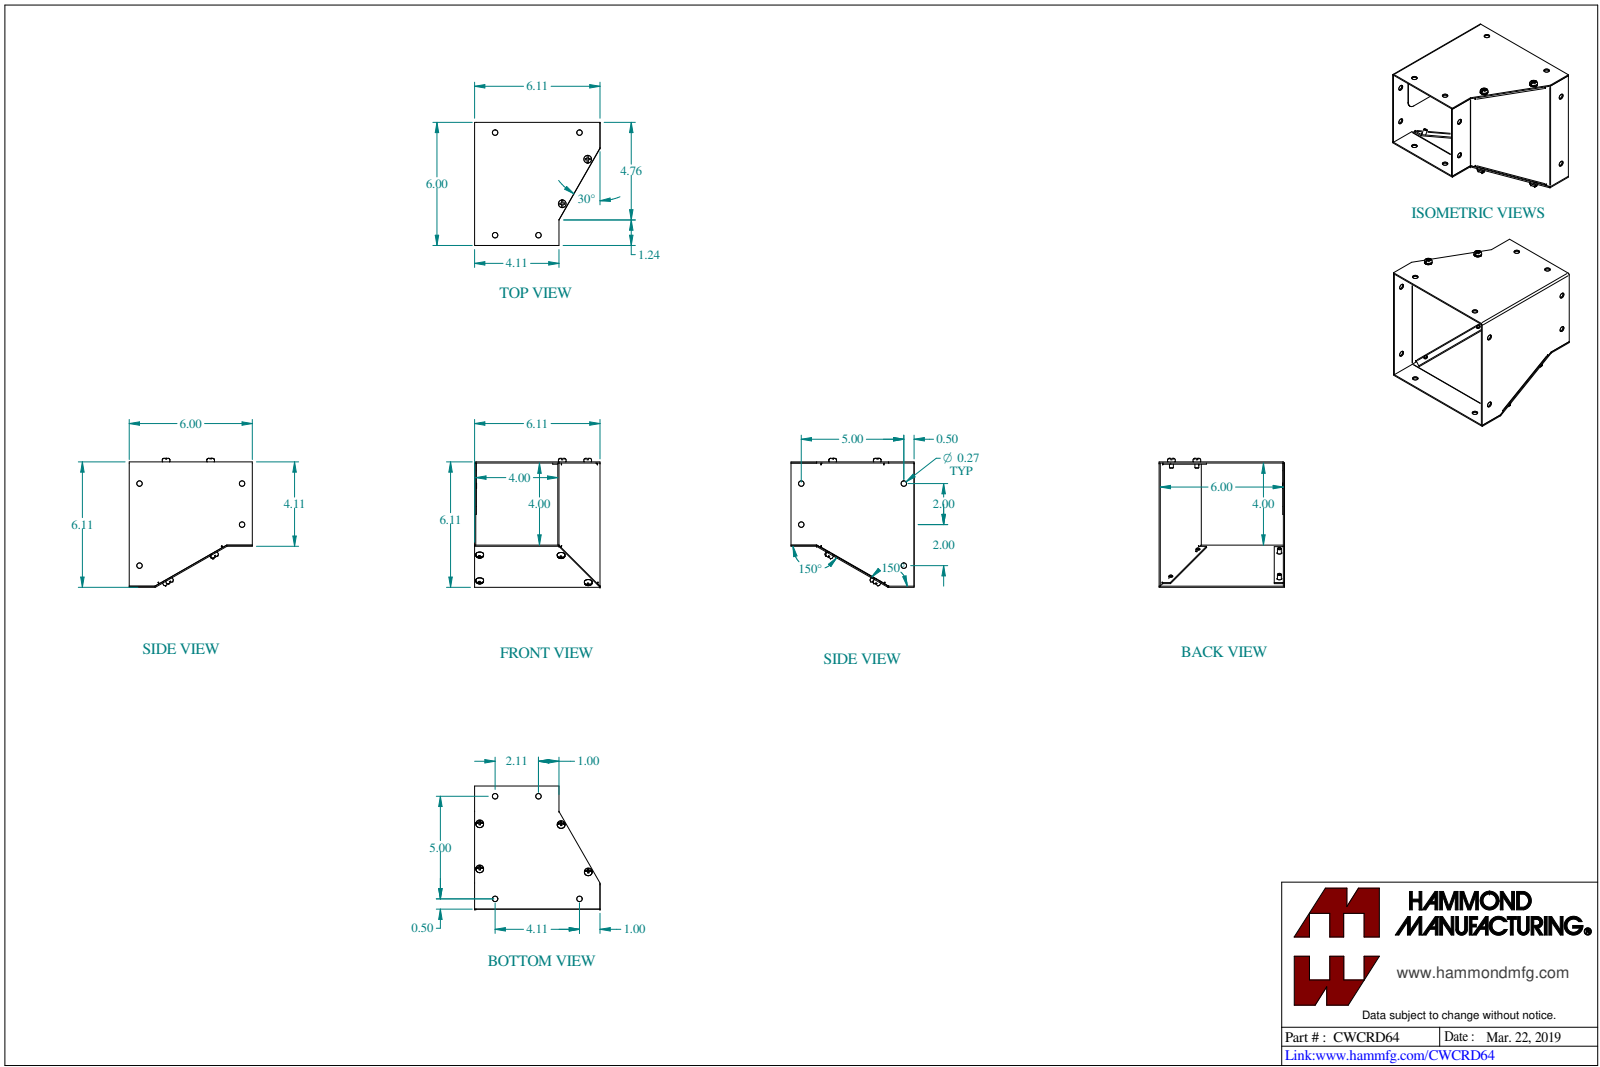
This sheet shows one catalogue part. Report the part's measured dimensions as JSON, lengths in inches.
{"part_name": "CWCRD64", "step_written_by": "SolidWorks 2023 (CONFIG_CONTROL_DESIGN)", "units": "inches", "bodies": {"solids": 9, "faces": 302, "planar": 168, "cylindrical": 96, "other": 38}, "overall_size": [6.289, 6.114, 6], "volume_in3": 7.541, "surface_area_in2": 269.3, "round_holes": [[0.266, 8], [0.17, 6], [0.25, 6]], "round_bosses_or_shafts": [[0.375, 6], [0.19, 6]], "partial_cylinders_radius": [[0.029, 8], [0.086, 8]], "face_to_face_distances": [0.057, 6.057, 2, 4.057, 6, 6.114, 4, 2.057, 1.943, 4.114], "hole_center_spacings": [2.502, 5.385, 1.921, 2.531, 2.969, 3.614, 5, 5.839]}
